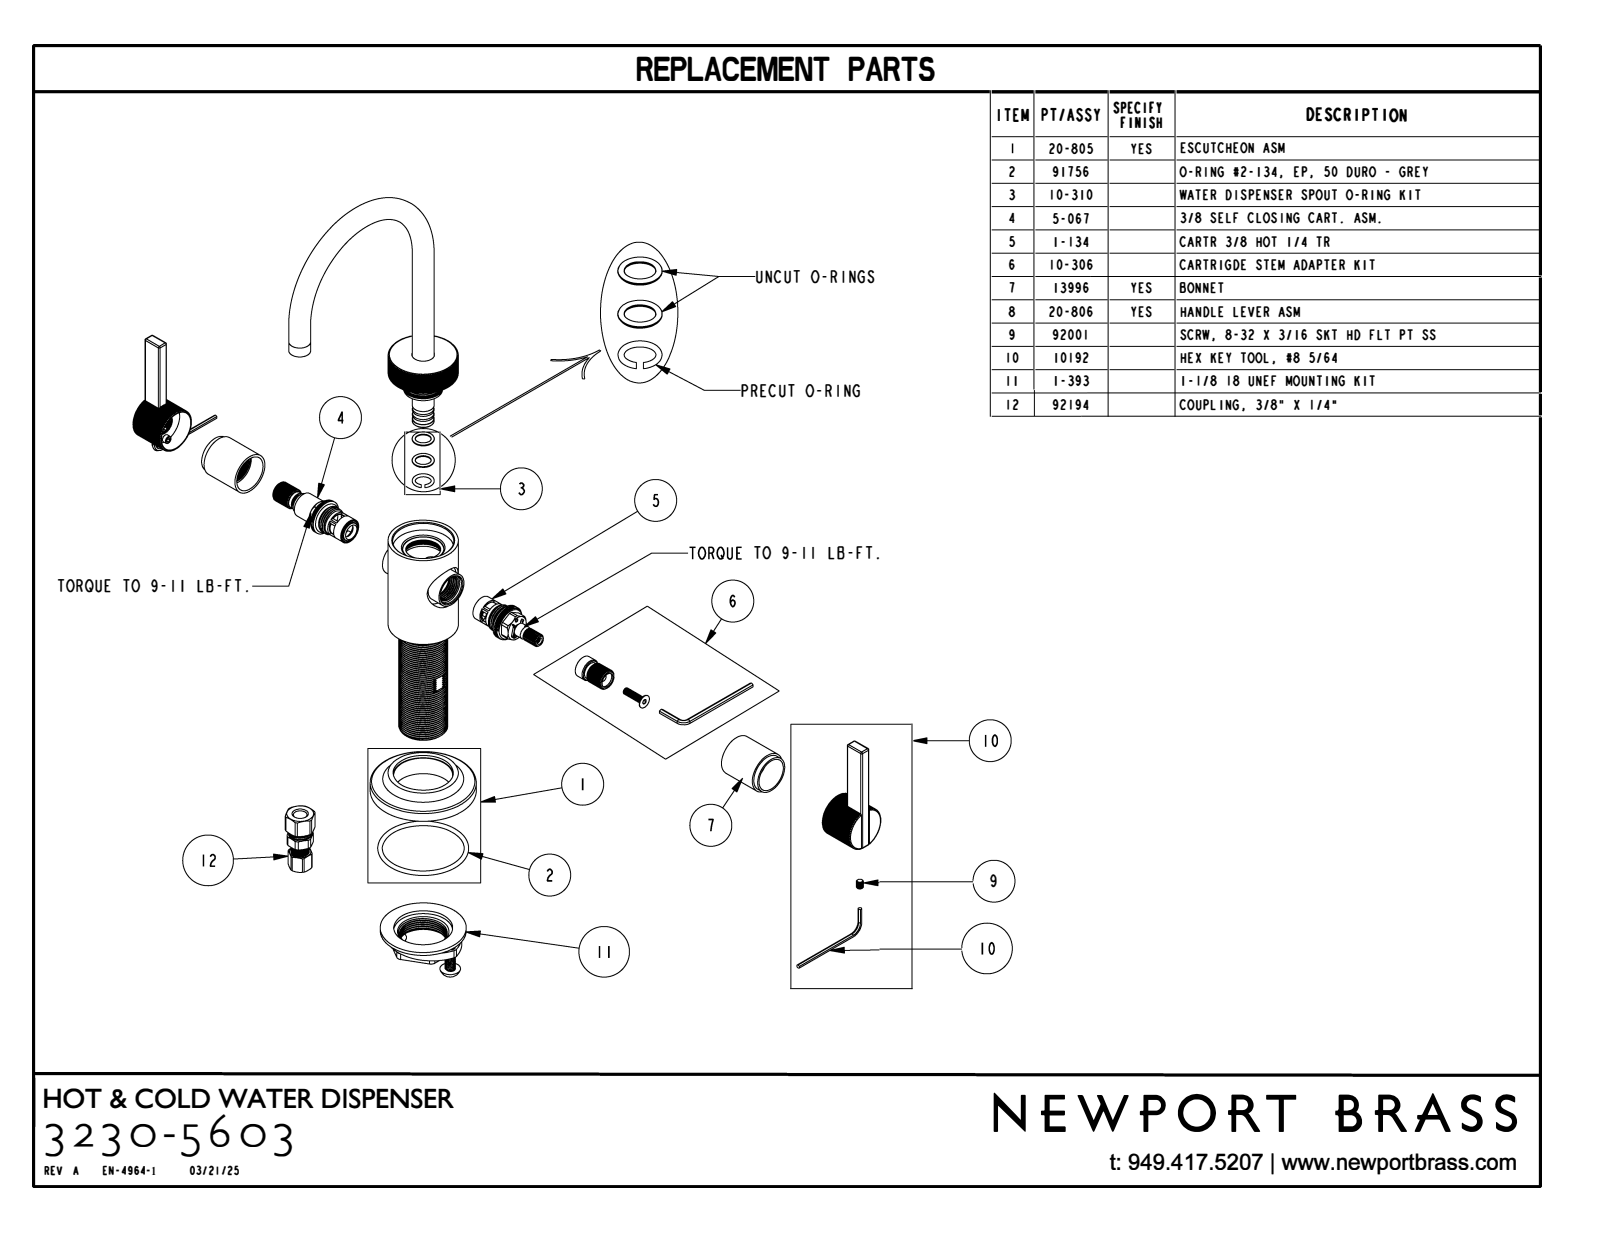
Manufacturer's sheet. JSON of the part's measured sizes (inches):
{"part_name": "3230-5603", "step_written_by": "CREO PARAMETRIC BY PTC INC, 2023134 (CONFIG_CONTROL_DESIGN)", "units": "inches", "bodies": {"solids": 1, "faces": 977, "planar": 573, "cylindrical": 342, "other": 62}, "overall_size": [9.4, 5.465, 5.002], "volume_in3": 11.4, "surface_area_in2": 82.4, "round_holes": [[0.067, 4], [0.4, 2], [0.2, 1], [0.253, 1], [0.37, 1], [0.52, 1], [0.615, 1], [1, 1]], "round_bosses_or_shafts": [[0.5, 2], [2.43, 1], [1.61, 1], [0.97, 1], [0.875, 1], [0.38, 1]], "partial_cylinders_radius": [[0.03, 20], [0.06, 4], [0.515, 1]], "face_to_face_distances": [0.257, 0.25, 3.381, 0.71, 0.711, 0.48, 4.522, 5.002, 0.265, 4.042], "hole_center_spacings": [0.185, 0.262, 0.37, 4.004, 3.815, 4, 4.185]}
